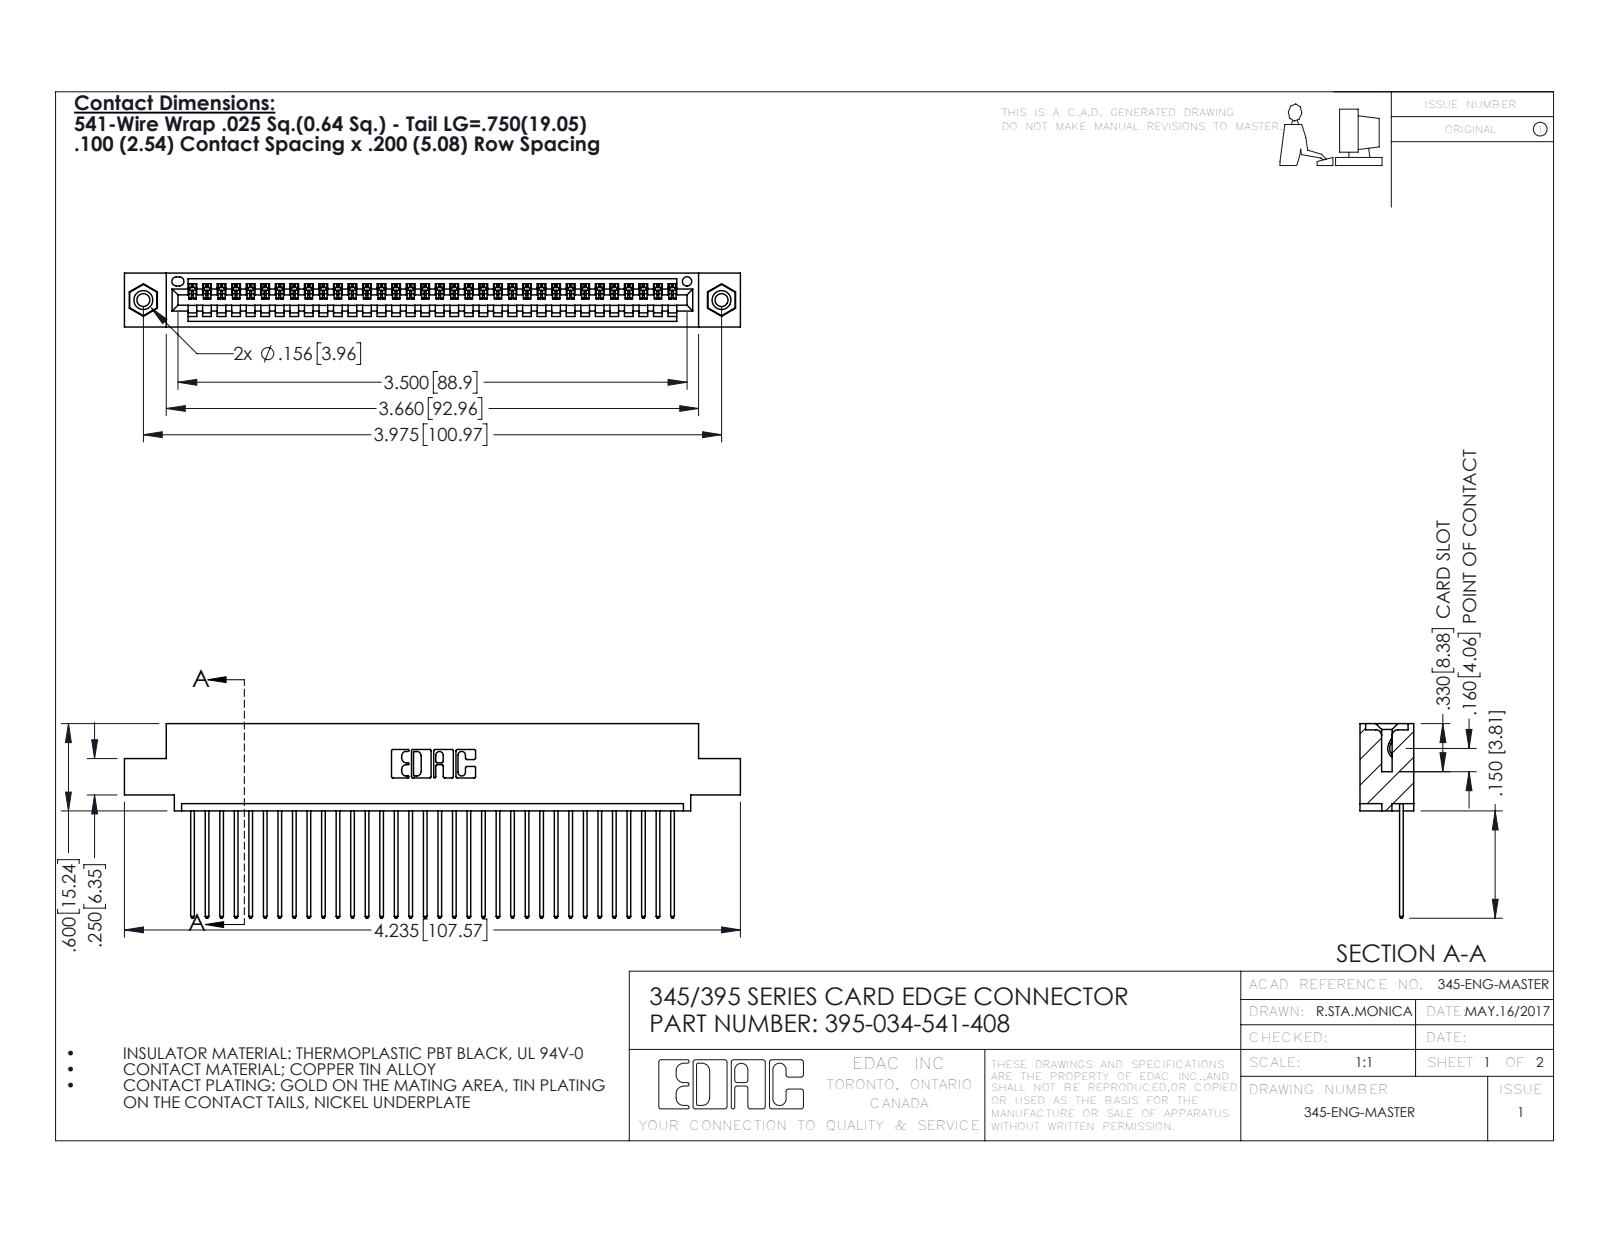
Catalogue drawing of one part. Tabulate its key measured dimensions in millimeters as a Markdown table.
| quantity | value |
| --- | --- |
| part name | 395-034-541-408; 345-292-001_345-293-141; 345 Part_0.110 Offset - 0.156 Dia-TI; 345-250-001_345-250-003-102 |
| STEP written by | SolidWorks 2016 (CONFIG_CONTROL_DESIGN) |
| units | millimeters |
| bodies | 37 solids, 2162 faces (1476 planar, 670 cylindrical, 16 other) |
| overall size | 107.6 × 34 × 9.4 |
| volume | 10 200 mm³ |
| surface area | 14 190 mm² |
| round holes (diameter × count) | 2.3 × 2, 3.2 × 2, 4 × 2, 1.6 × 1 |
| round bosses / shafts (diameter × count) | 3.9 × 2 |
| partial cylindrical surfaces (radius × count) | 0.2 × 68, 0.3 × 68, 0.3 × 22, 0.2 × 6, 0.8 × 6, 0.7 × 3, 0.8 × 2, 1 × 2 |
| main face-to-face distances | 1.8, 7.6, 2.5, 6.9, 0.6, 9.4, 5.1, 5.7, 3.8, 1.8 |
| hole center spacings | 6.9, 95, 101 |
